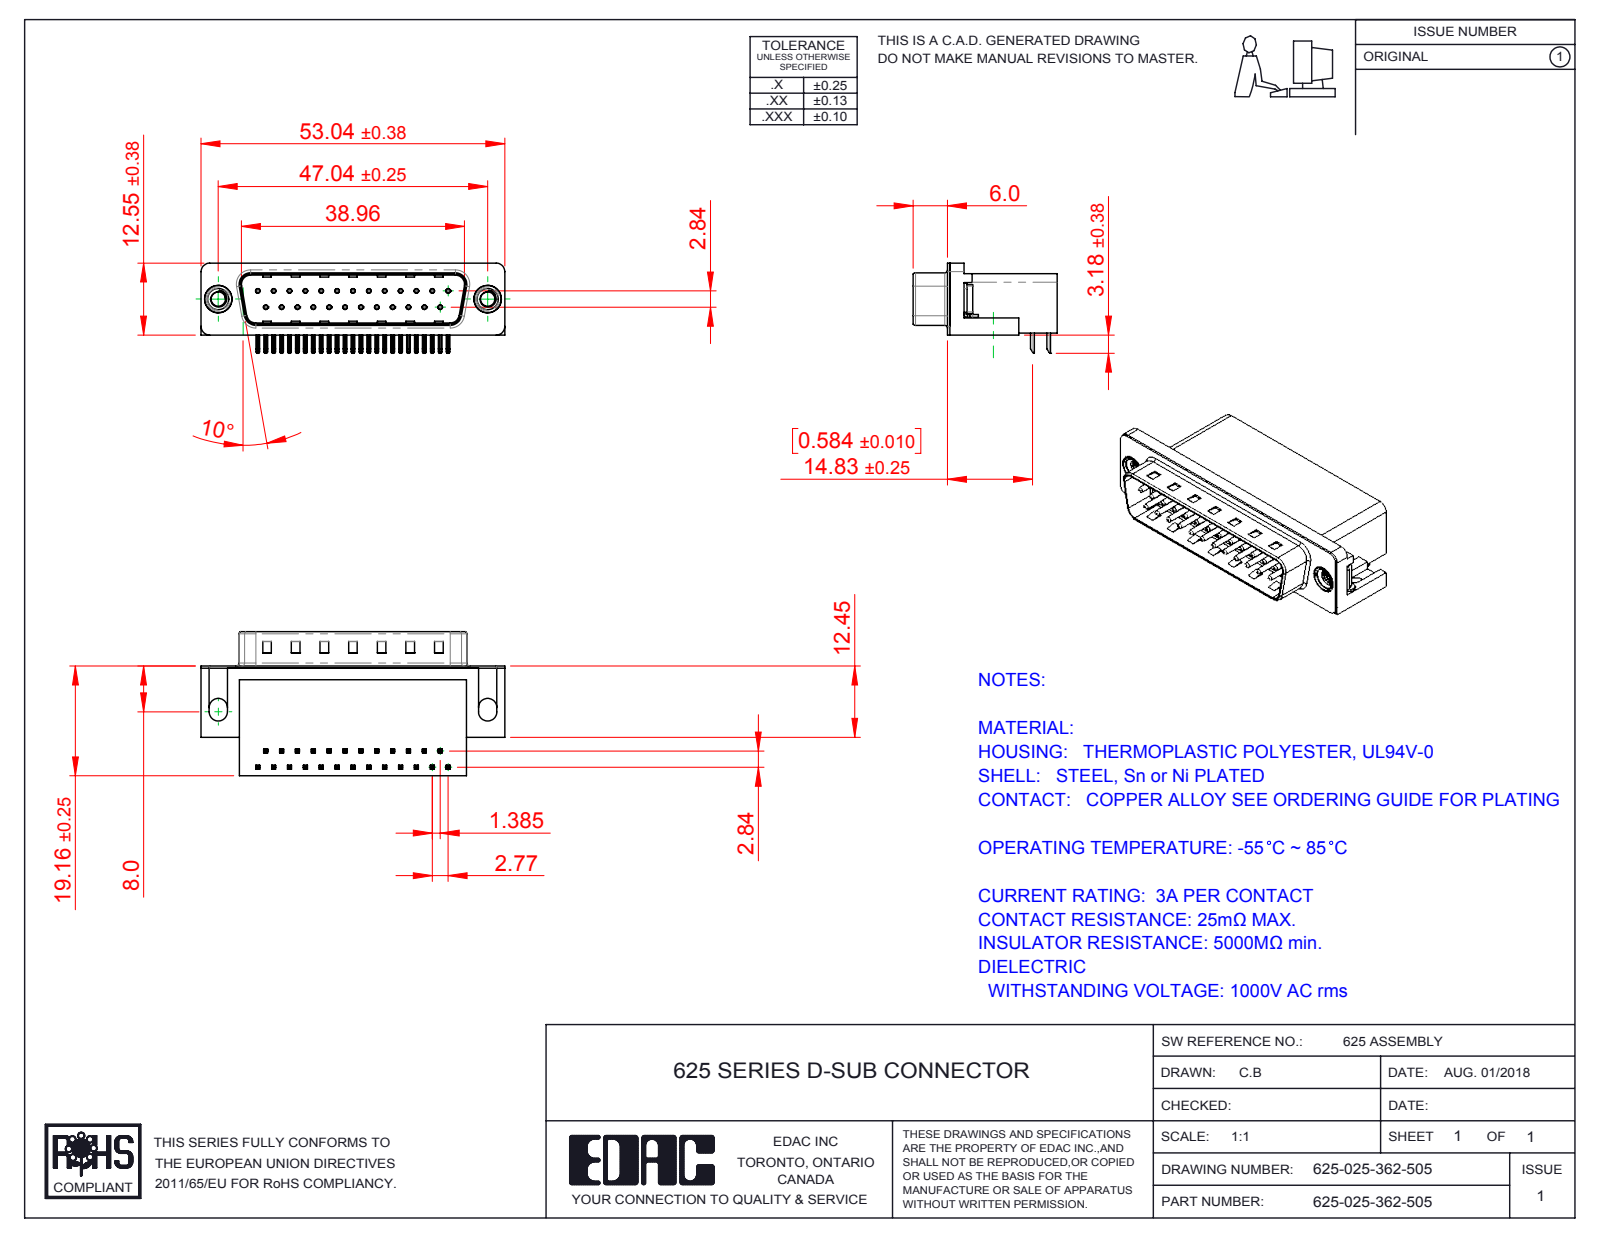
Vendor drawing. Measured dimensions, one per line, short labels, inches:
name: 625 Contact Bottom; 625 Housing_25 Socket; 625-025-362-505; 625 Contact Top (+3 more)
written by: SolidWorks 2016 (CONFIG_CONTROL_DESIGN)
unit: in
bodies: 31 solids, 2263 faces (1407 planar, 661 cylindrical, 195 other)
size: 2.088 × 0.991 × 0.619
volume: 0.557 in³; area: 13.53 in²
holes: 25× ⌀0.014, 25× ⌀0.031, 2× ⌀0.098, 2× ⌀0.157, 2× ⌀0.189, 2× ⌀0.197
bosses: 25× ⌀0.03, 2× ⌀0.193, 2× ⌀0.187, 2× ⌀0.154
rounds: 108× R0.01, 50× R0.005, 16× R0.039, 9× R0.02, 8× R0.063, 7× R0.059, 4× R0.035, 4× R0.079
face distances: 0.016, 0.407, 0.739, 0.083, 0.345, 0.412, 0.428, 0.067, 0.754, 0.398
hole spacings: 0.124, 0.109, 0.436, 0.218, 0.327, 0.198, 0.545, 0.294
